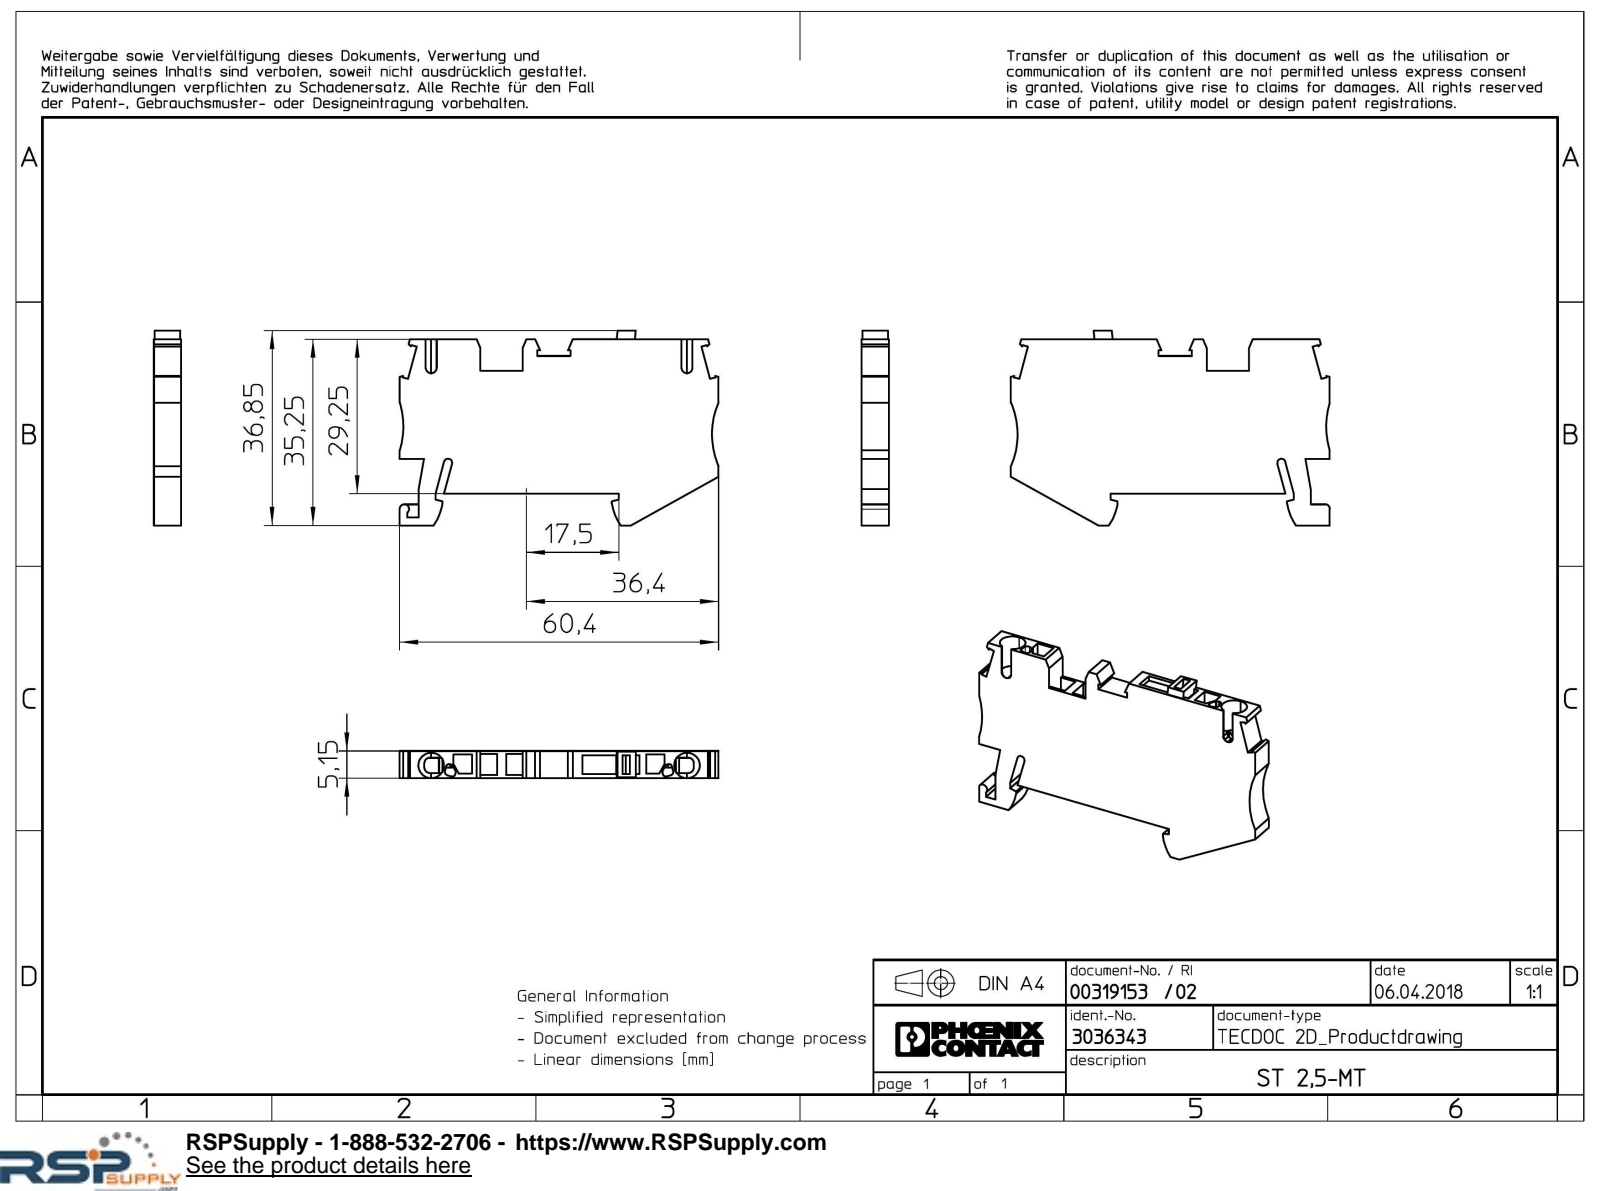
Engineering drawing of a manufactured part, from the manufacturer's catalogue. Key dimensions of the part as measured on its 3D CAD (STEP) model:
Part name (STEP PRODUCT): ST_2.5_MT-select
STEP written by: Creo Elements/Direct Modeling 18.1I 14-Aug-2016 (C) Parametric Technology GmbH (AUTOMOTIVE_DESIGN)
Units: millimetres
Bodies: 1 solid, 181 faces (140 planar, 31 cylindrical, 10 other)
Overall size (bounding box): 60.4 × 36.85 × 5.15
Volume: 7 711 mm³ · Surface area: 5 769 mm²
Partial cylindrical surfaces — rounded edges, fillets, slot ends (radius × count): R1 ×8, R0.3 ×4, R2.4 ×4, R0.5 ×2, R0.6 ×2, R0.67 ×2, R9.5 ×2, R11.94 ×2
Main face-to-face distances: 5.15, 29.25, 4.85, 0.65, 3.15, 4, 4.57, 0.58, 0.57, 4.58
